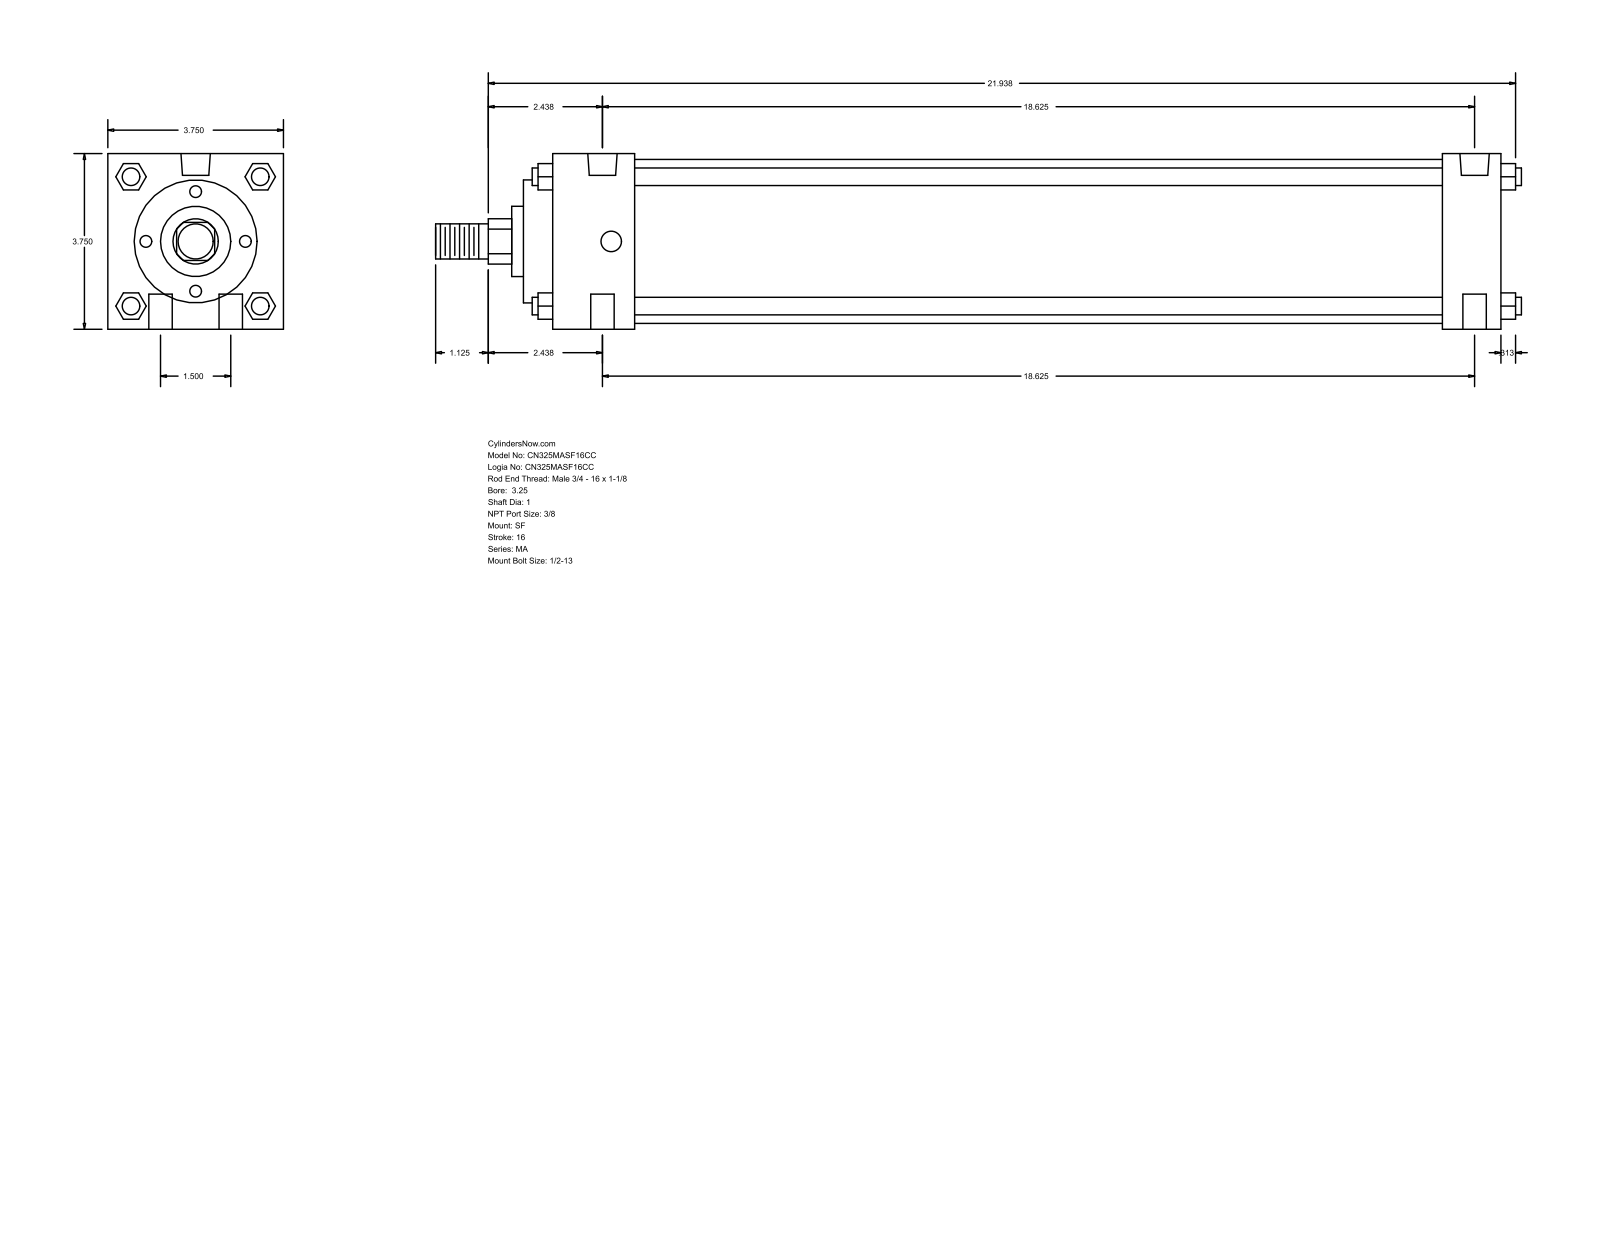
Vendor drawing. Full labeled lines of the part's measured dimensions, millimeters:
Part name (STEP PRODUCT): MA_SF__0325_1
STEP written by: GSSL Pune (CONFIG_CONTROL_DESIGN)
Units: millimetres
Bodies: 0 solids, 126 faces (95 planar, 31 cylindrical, 0 other)
Overall size (bounding box): 588.96 × 95.25 × 95.25
Round holes (diameter × count): ⌀12.7 ×4, ⌀11.11 ×2, ⌀15.93 ×2
Round bosses / shafts (diameter × count): ⌀9.53 ×4, ⌀88.9 ×1, ⌀66.67 ×1, ⌀38.1 ×1, ⌀25.4 ×1, ⌀19.05 ×1
Partial cylindrical surfaces — rounded edges, fillets, slot ends (radius × count): R12.29 ×1
Main face-to-face distances: 95.24, 514.35, 530.22, 482.6, 31.75, 44.46, 438.14, 469.89, 15.87, 60.33
Hole centre spacings: 19.05, 473.46, 473.08, 38.1, 474.61, 463.56
